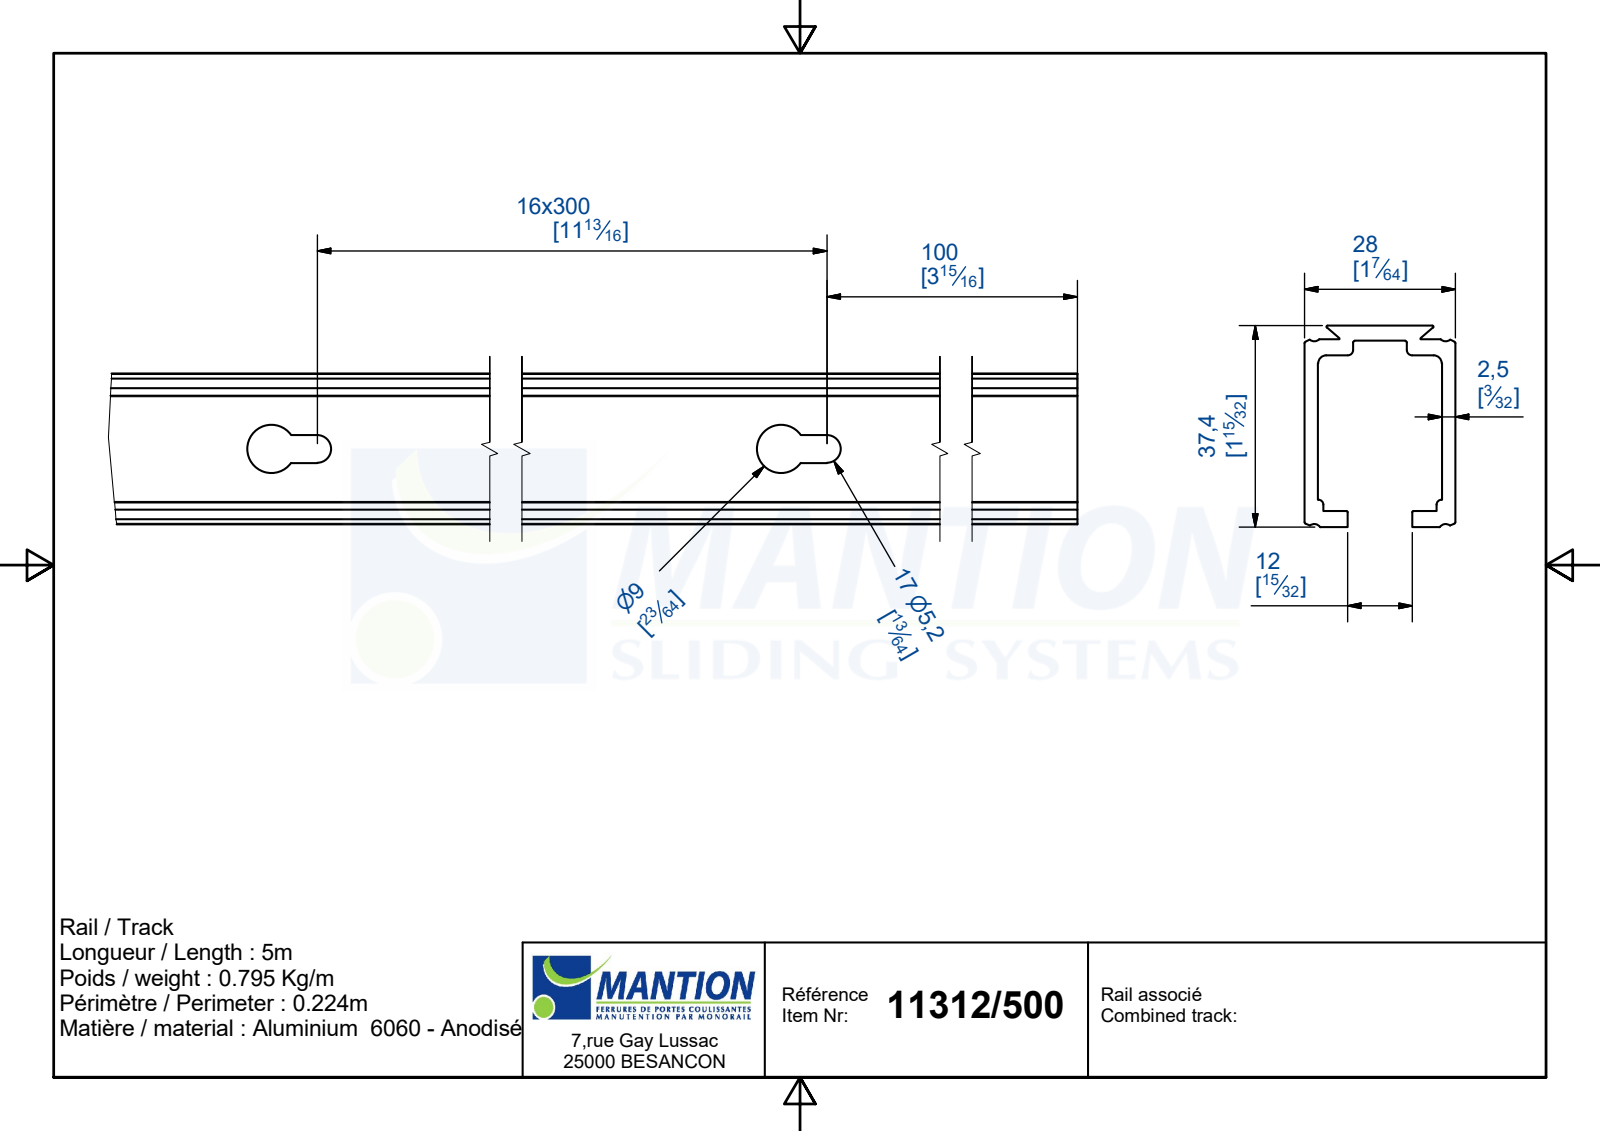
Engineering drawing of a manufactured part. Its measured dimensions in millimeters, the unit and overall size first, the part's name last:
Units: millimetres
Overall size (bounding box): 5000 × 37.4 × 28
Round holes (diameter × count): ⌀9 ×17
Partial cylindrical surfaces — rounded edges, fillets, slot ends (radius × count): R2.6 ×17, R0.3 ×6, R0.2 ×4, R1.3 ×4, R0.9 ×2, R1 ×2, R1.5 ×2
Main face-to-face distances: 2.5, 25.5, 28, 23, 3, 5.5, 31.9, 37.4, 34.6, 2.8
Hole centre spacings: 300, 600, 900, 1200, 1500, 1800, 2100, 2400
Volume: 1 462 000 mm³ · Surface area: 1 120 000 mm²
Bodies: 1 solid, 120 faces (66 planar, 54 cylindrical, 0 other)
Part name (STEP PRODUCT): 11312
STEP written by: Autodesk Inventor 2019 (AUTOMOTIVE_DESIGN)
